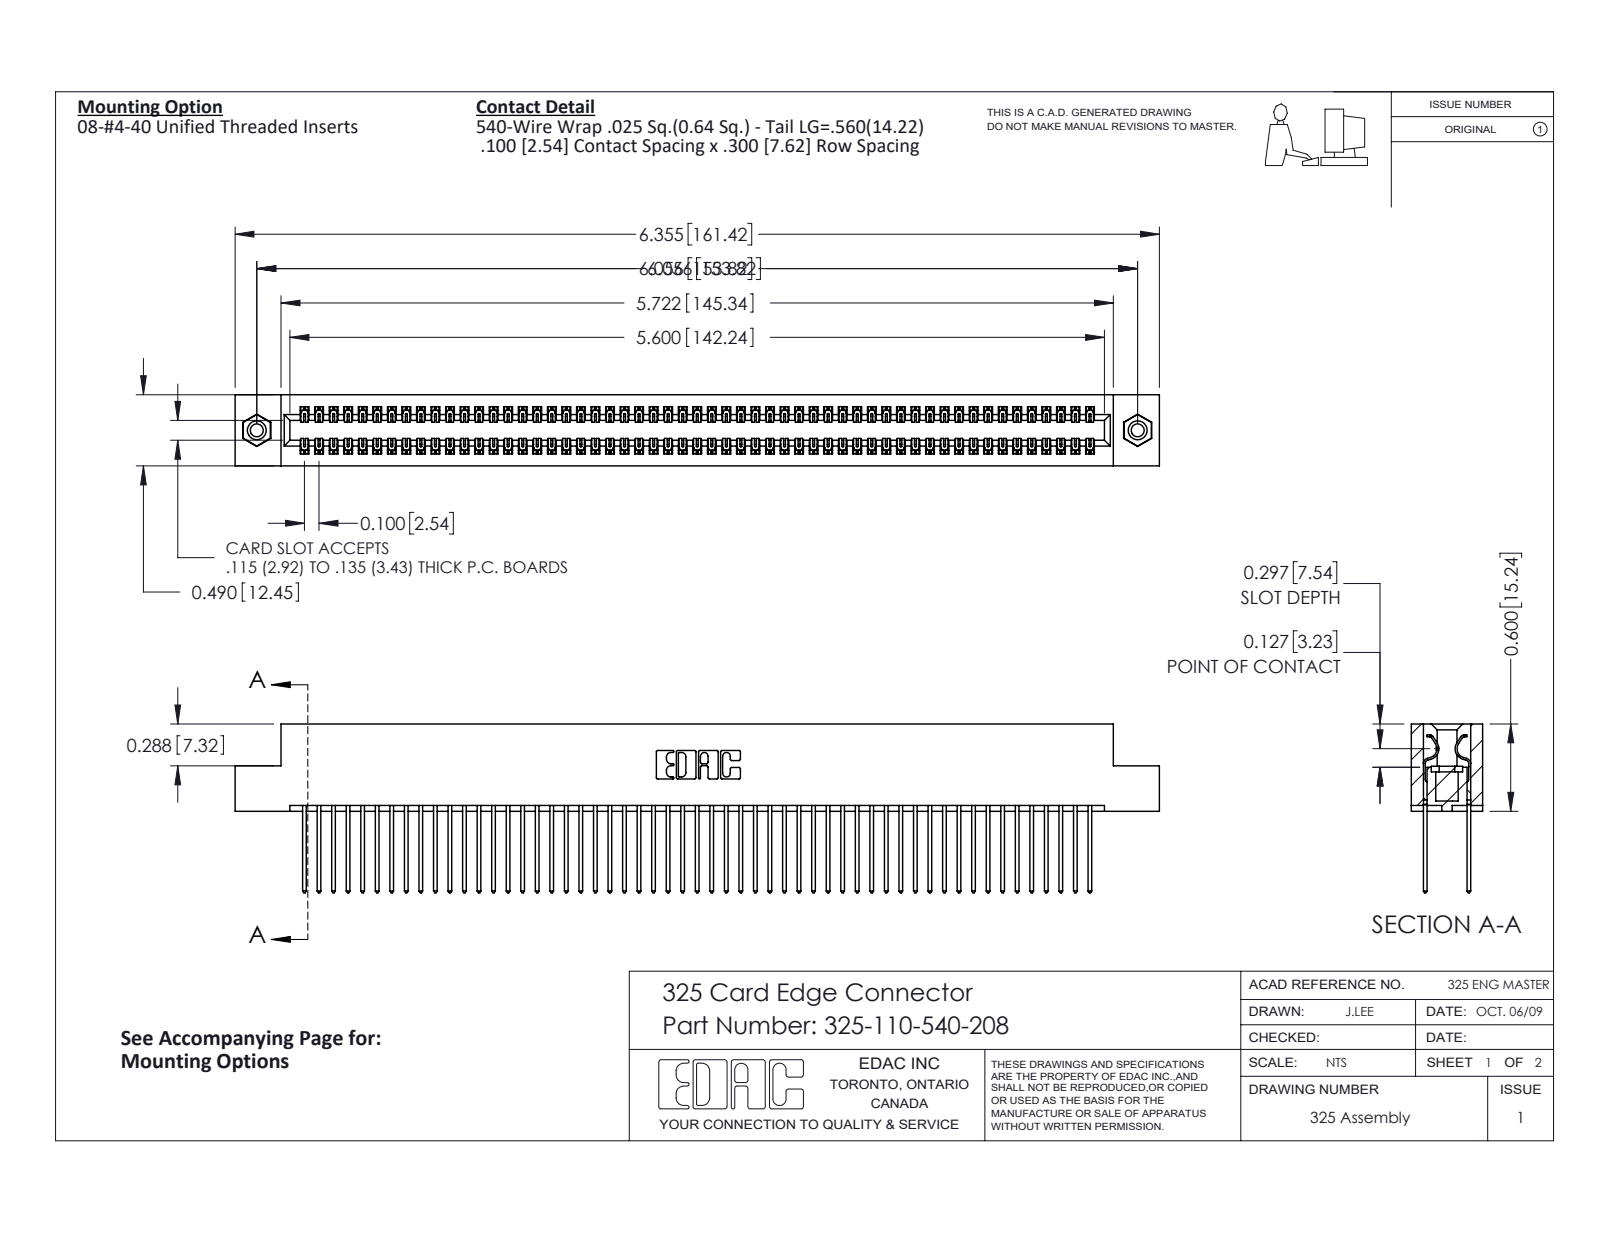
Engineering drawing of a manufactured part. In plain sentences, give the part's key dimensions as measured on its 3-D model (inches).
The part is named "325-292-001_325-293-140; 325-110-540-208; 325 Part_TI; 345-250-001_345-250-003-102". Its 3-D file was written by "SolidWorks 2016 (CONFIG_CONTROL_DESIGN)". It is 113 solids with 5894 faces: 4062 planar, 1816 cylindrical and 16 other. Overall it measures 6.355 by 1.16 by 0.49 inches. Its volume is 1.304 cubic inches and its surface area 43.66 square inches. Round holes: 2 of diameter 0.089, 2 of diameter 0.125, 2 of diameter 0.16. Round bosses or shafts: 2 of diameter 0.155. Partial cylindrical surfaces (rounded edges, fillets, slot ends): 165 of radius 0.006, 110 of radius 0.01, 22 of radius 0.01, 6 of radius 0.007, 6 of radius 0.031, 3 of radius 0.026, 2 of radius 0.014, 2 of radius 0.022. The main face-to-face distances are 0.083, 0.407, 0.3, 0.107, 0.383, 0.025, 0.325, 0.49, 0.275, 0.56. The hole center spacings are 6.056.
